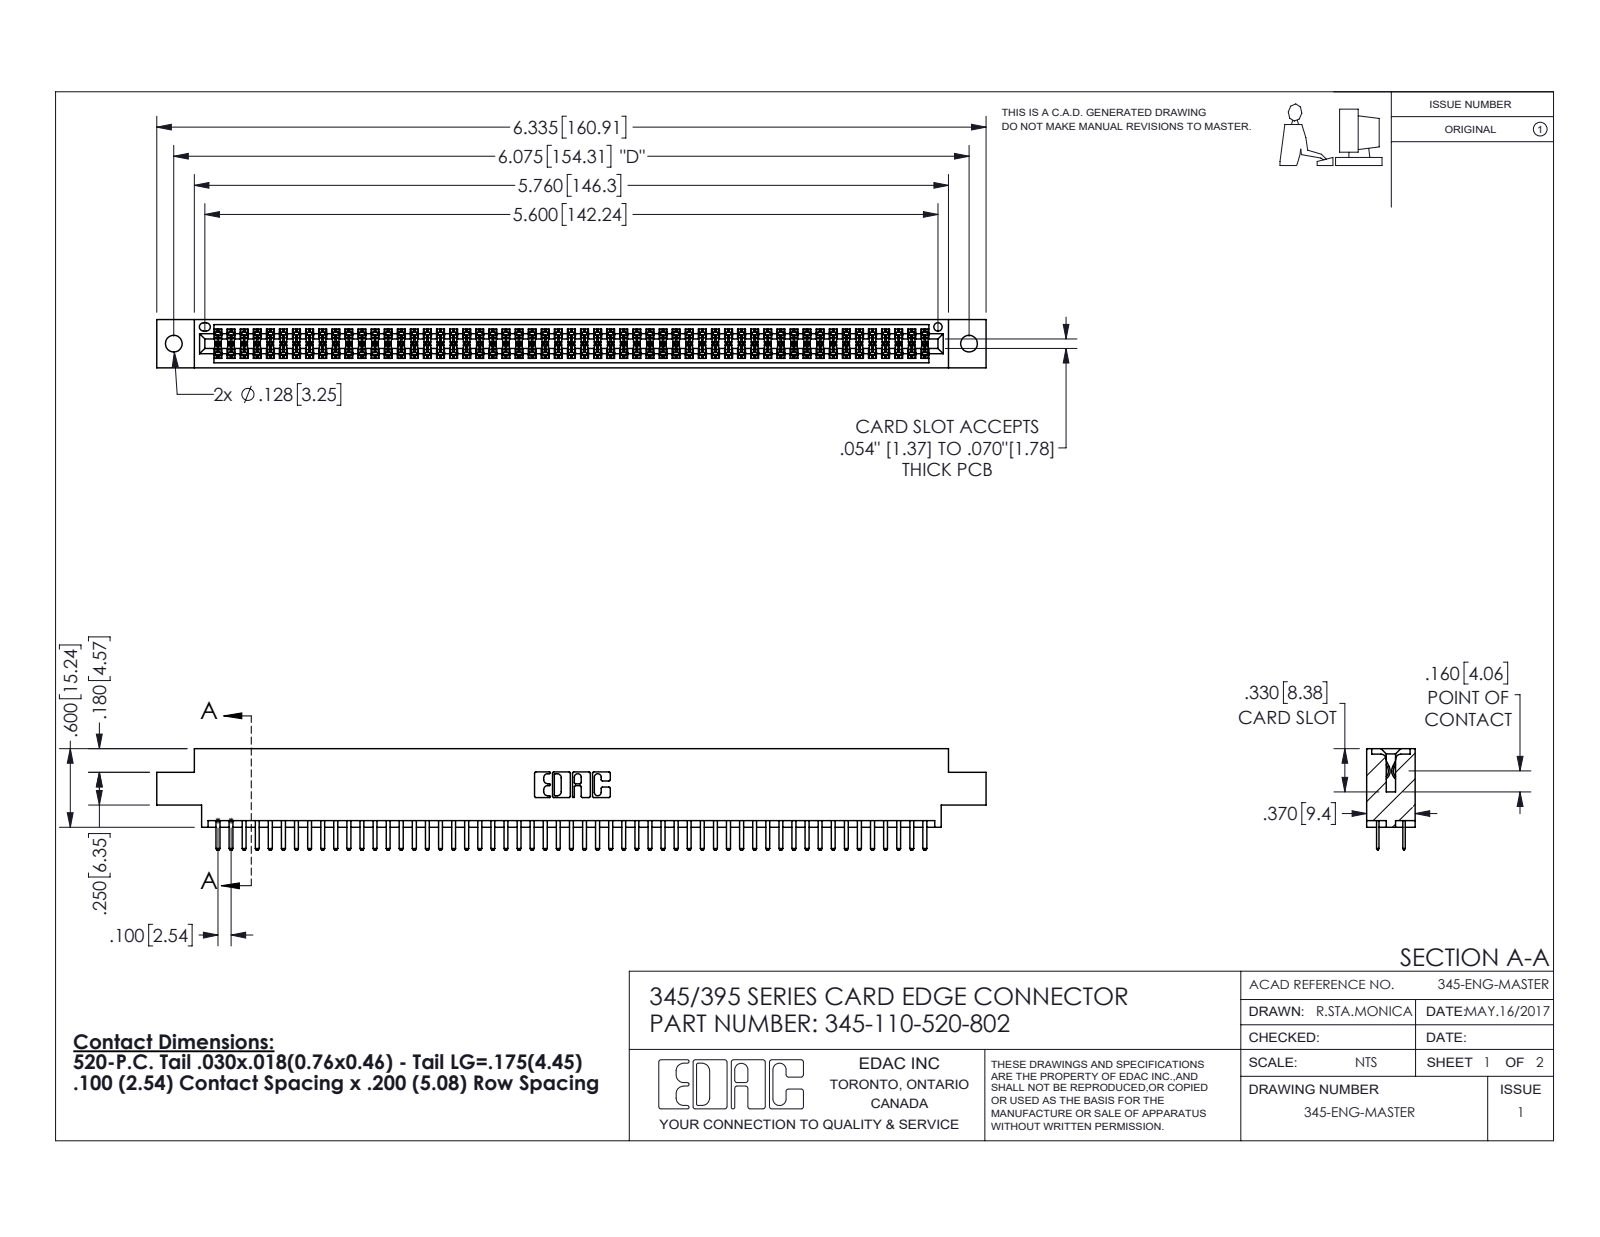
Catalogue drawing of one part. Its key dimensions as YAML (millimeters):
part_name: "345-292-001_345-293-120; 345 Part_0.170 Offset - 0.128 Dia; 345-110-520-802"
step_written_by: "SolidWorks 2016 (CONFIG_CONTROL_DESIGN)"
units: millimeters
bodies: {solids: 111, faces: 6070, planar: 3934, cylindrical: 2136, other: 0}
overall_size: [160.9, 19.7, 9.4]
volume: 15600
surface_area: 23010
round_holes:
  - {diameter: 3.3, count: 2}
  - {diameter: 1.6, count: 1}
partial_cylinders:
  - {radius: 0.2, count: 165}
  - {radius: 0.3, count: 114}
  - {radius: 0.3, count: 22}
  - {radius: 0.2, count: 6}
  - {radius: 0.8, count: 6}
  - {radius: 0.7, count: 3}
  - {radius: 0.4, count: 2}
  - {radius: 0.5, count: 2}
face_to_face_distances: [1.8, 7.6, 5.1, 9.4, 2.5, 6.9, 0.6, 5.7, 0.6, 1.8]
hole_center_spacings: [6.9, 148.3, 154.3]
